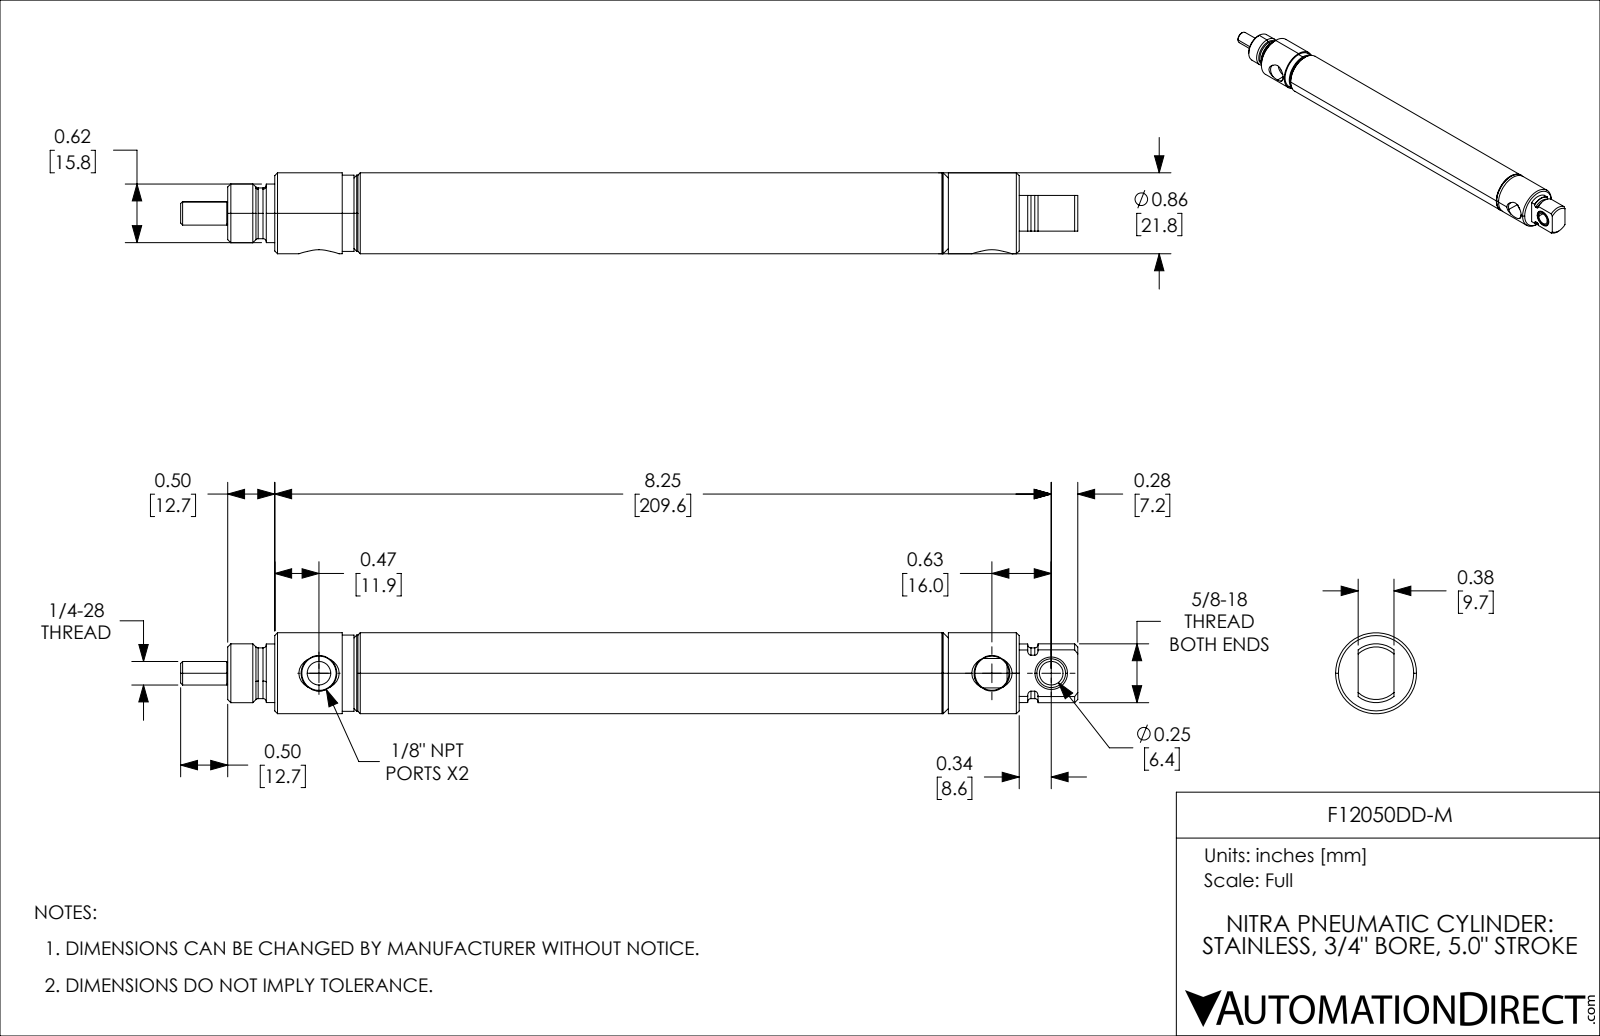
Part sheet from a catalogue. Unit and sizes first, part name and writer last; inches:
Units: inches
Overall size (bounding box): 9.532 × 0.86 × 0.86
Round holes (diameter × count): ⌀0.25 ×1, ⌀0.251 ×1, ⌀0.274 ×1, ⌀0.312 ×1, ⌀0.346 ×1, ⌀0.363 ×1, ⌀0.5 ×1, ⌀0.702 ×1
Round bosses / shafts (diameter × count): ⌀0.86 ×1, ⌀0.81 ×1, ⌀0.762 ×1, ⌀0.625 ×1, ⌀0.622 ×1, ⌀0.539 ×1, ⌀0.25 ×1, ⌀0.23 ×1
Partial cylindrical surfaces — rounded edges, fillets, slot ends (radius × count): R0.269 ×1
Main face-to-face distances: 0.844, 1.594, 7.438, 5, 5.844, 6.816, 1.816, 0.972, 0.5, 0.38
Hole centre spacings: 0.63, 7.15, 7.78
Volume: 2.657 in³ · Surface area: 54.88 in²
Bodies: 5 solids, 158 faces (29 planar, 61 cylindrical, 68 other)
Part name (STEP PRODUCT): F12050DD-M_11; F12050DD-M_3; F12050DD-M_7; F12050DD-M_5 (+2 more)
STEP written by: SolidWorks 2021 (CONFIG_CONTROL_DESIGN)
